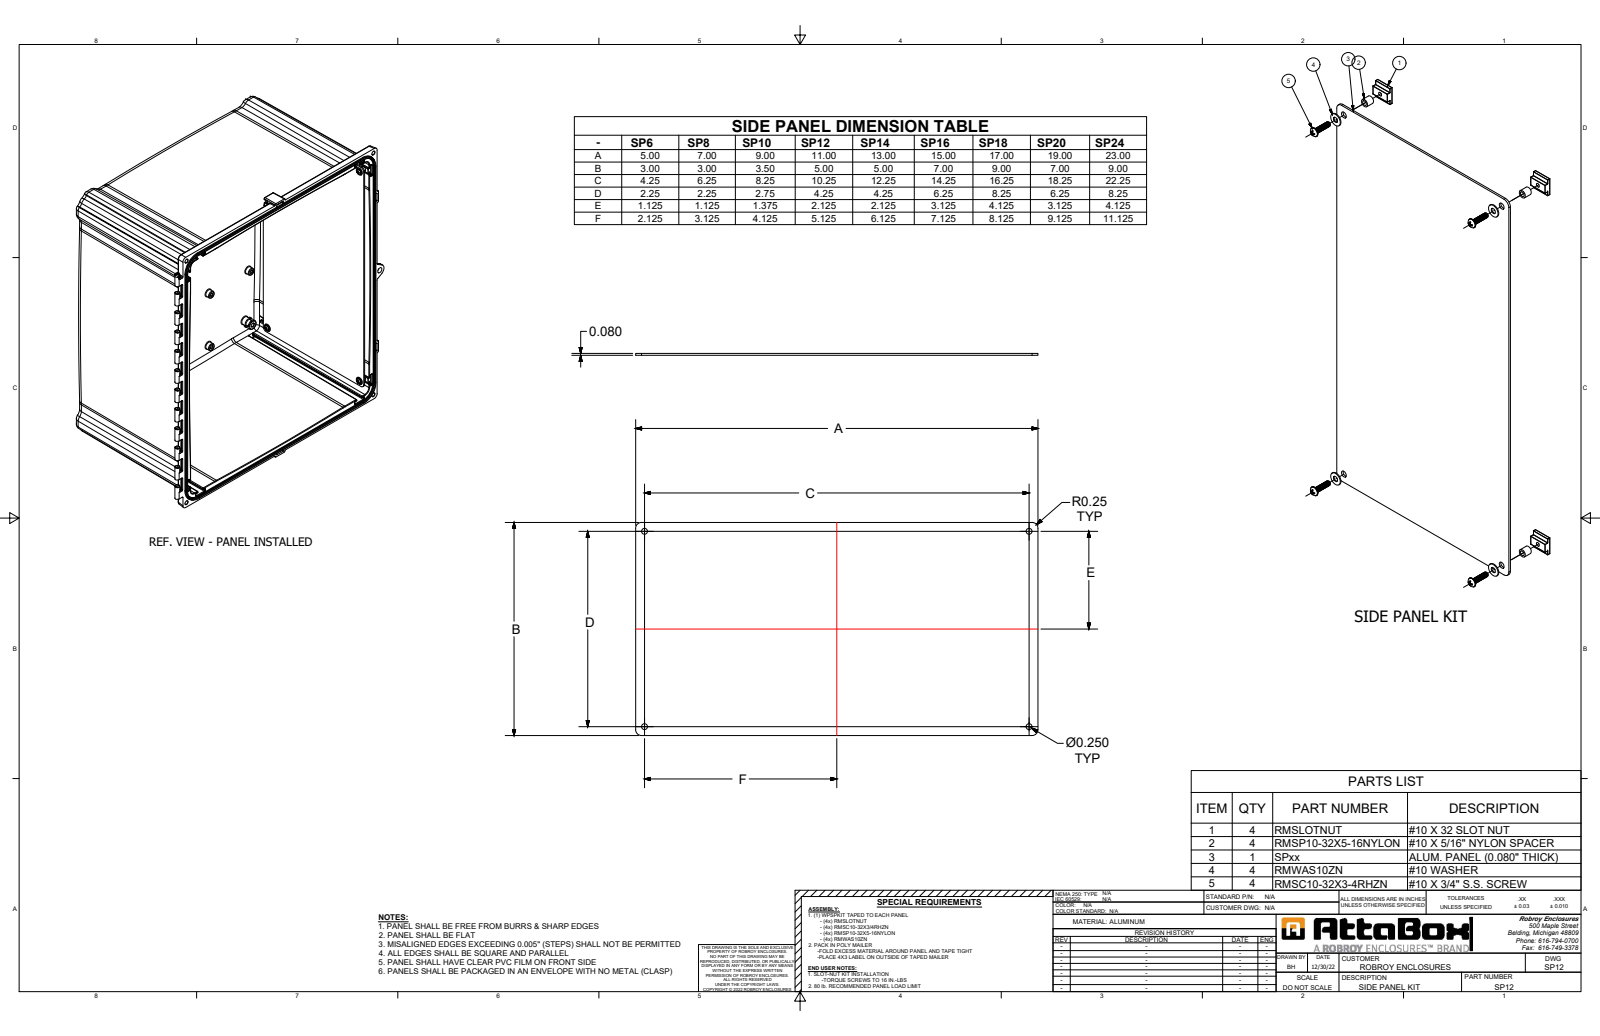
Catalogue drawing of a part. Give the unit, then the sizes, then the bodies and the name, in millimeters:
Units: millimetres
Overall size (bounding box): 279.4 × 127 × 2
Round holes (diameter × count): ⌀6.4 ×4
Partial cylindrical surfaces — rounded edges, fillets, slot ends (radius × count): R6.4 ×4
Main face-to-face distances: 2, 127, 279.4
Hole centre spacings: 108, 260.4, 281.8
Volume: 71 780 mm³ · Surface area: 72 450 mm²
Bodies: 1 solid, 14 faces (6 planar, 8 cylindrical, 0 other)
Part name (STEP PRODUCT): SP12_Default
STEP written by: SolidWorks 2023 (CONFIG_CONTROL_DESIGN)
